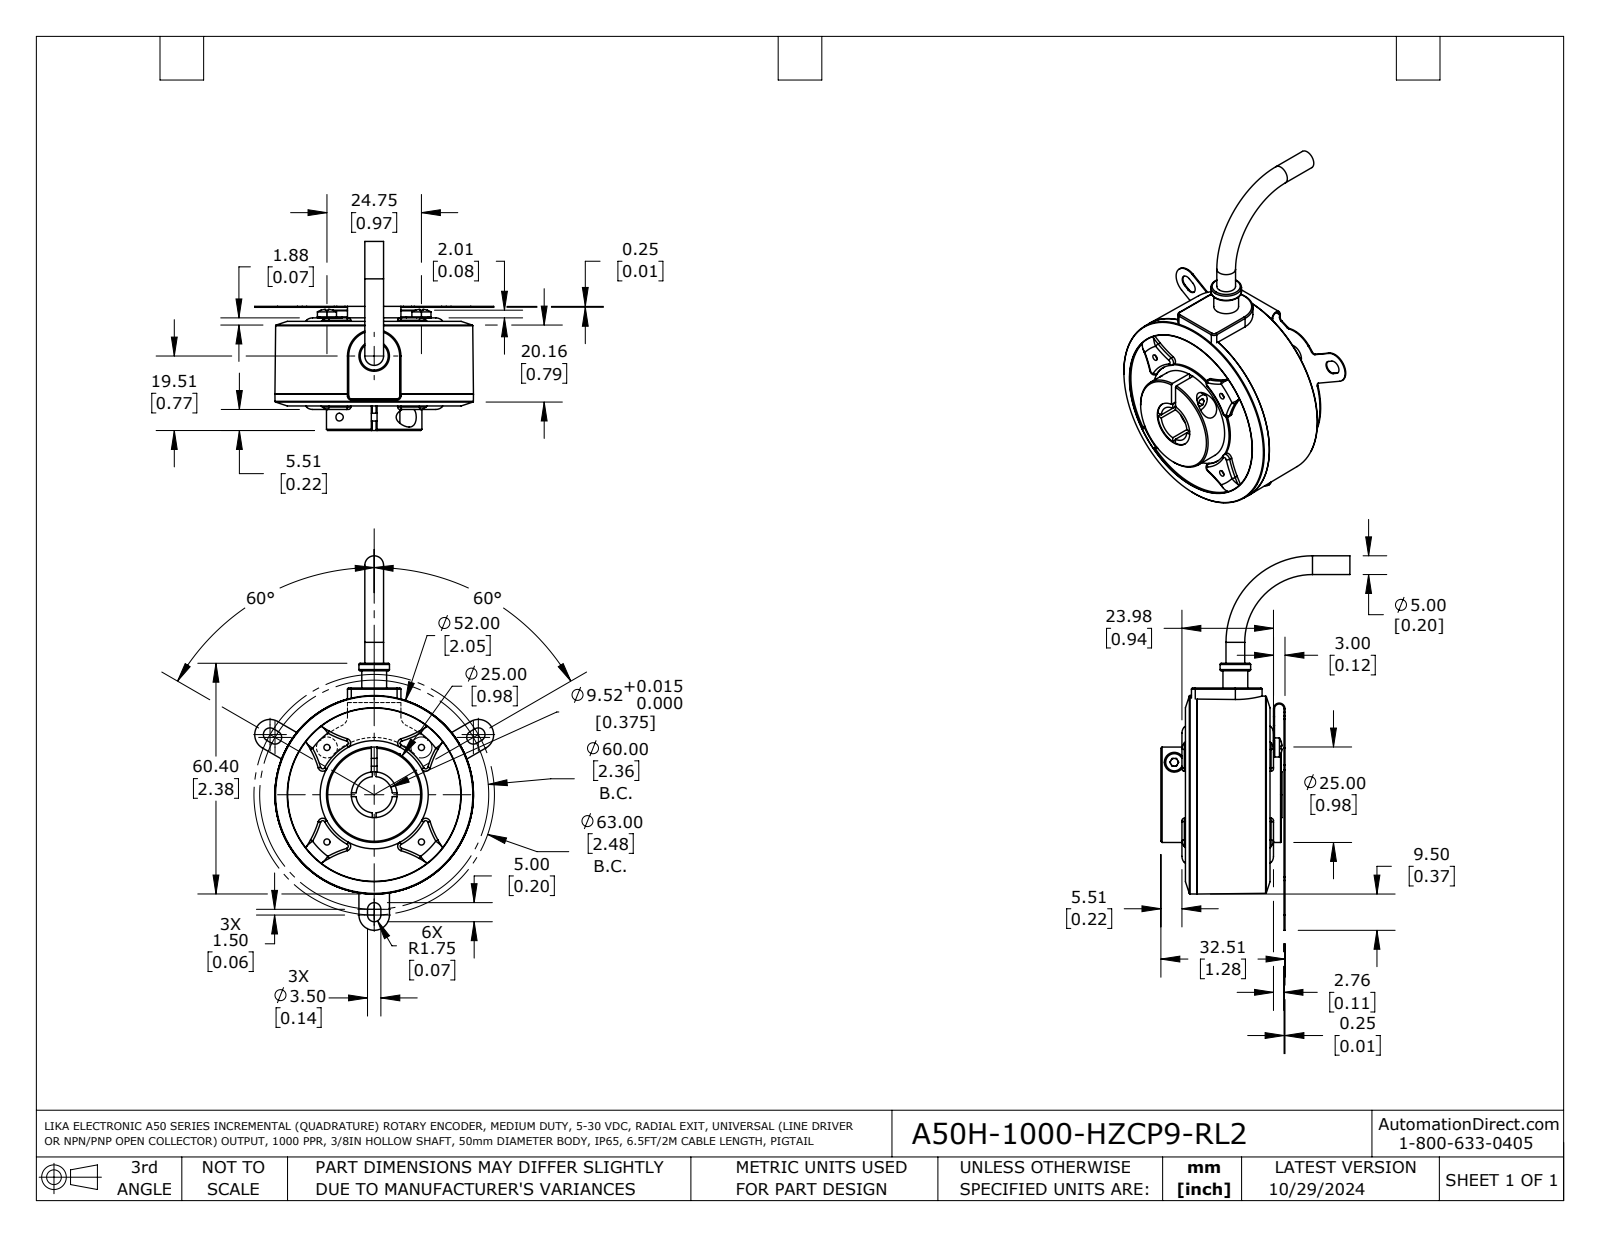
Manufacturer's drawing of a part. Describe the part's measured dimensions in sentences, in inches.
The part is named "A50H-1000-HZCP9-RL2". Its 3-D file was written by "SolidWorks 2021 (AUTOMOTIVE_DESIGN)". It is 8 solids with 504 faces: 168 planar, 160 cylindrical and 176 other. Overall it measures 3.86 by 2.464 by 1.949 inches. Its volume is 3.657 cubic inches and its surface area 31.76 square inches. Round holes: 4 of diameter 0.064, 3 of diameter 0.11, 2 of diameter 0.217, 1 of diameter 0.081, 1 of diameter 0.205, 1 of diameter 0.375, 1 of diameter 0.472, 1 of diameter 1.024, 1 of diameter 1.115, 1 of diameter 1.786. Round bosses or shafts: 4 of diameter 0.098, 2 of diameter 0.197, 2 of diameter 0.193, 1 of diameter 0.984, 1 of diameter 0.315, 1 of diameter 0.256, 1 of diameter 0.177. Partial cylindrical surfaces (rounded edges, fillets, slot ends): 12 of radius 0.039, 8 of radius 0.008, 6 of radius 0.008, 6 of radius 0.069, 3 of radius 0.157, 2 of radius 0.01, 2 of radius 0.013, 2 of radius 0.098. The main face-to-face distances are 0.896, 0.906, 0.154, 0.144, 0.751, 1.009, 0.999, 0.854, 0.103, 0.709. The hole center spacings are 0.583, 0.689, 0.974, 1.383, 0.807, 1.378, 1.614.
